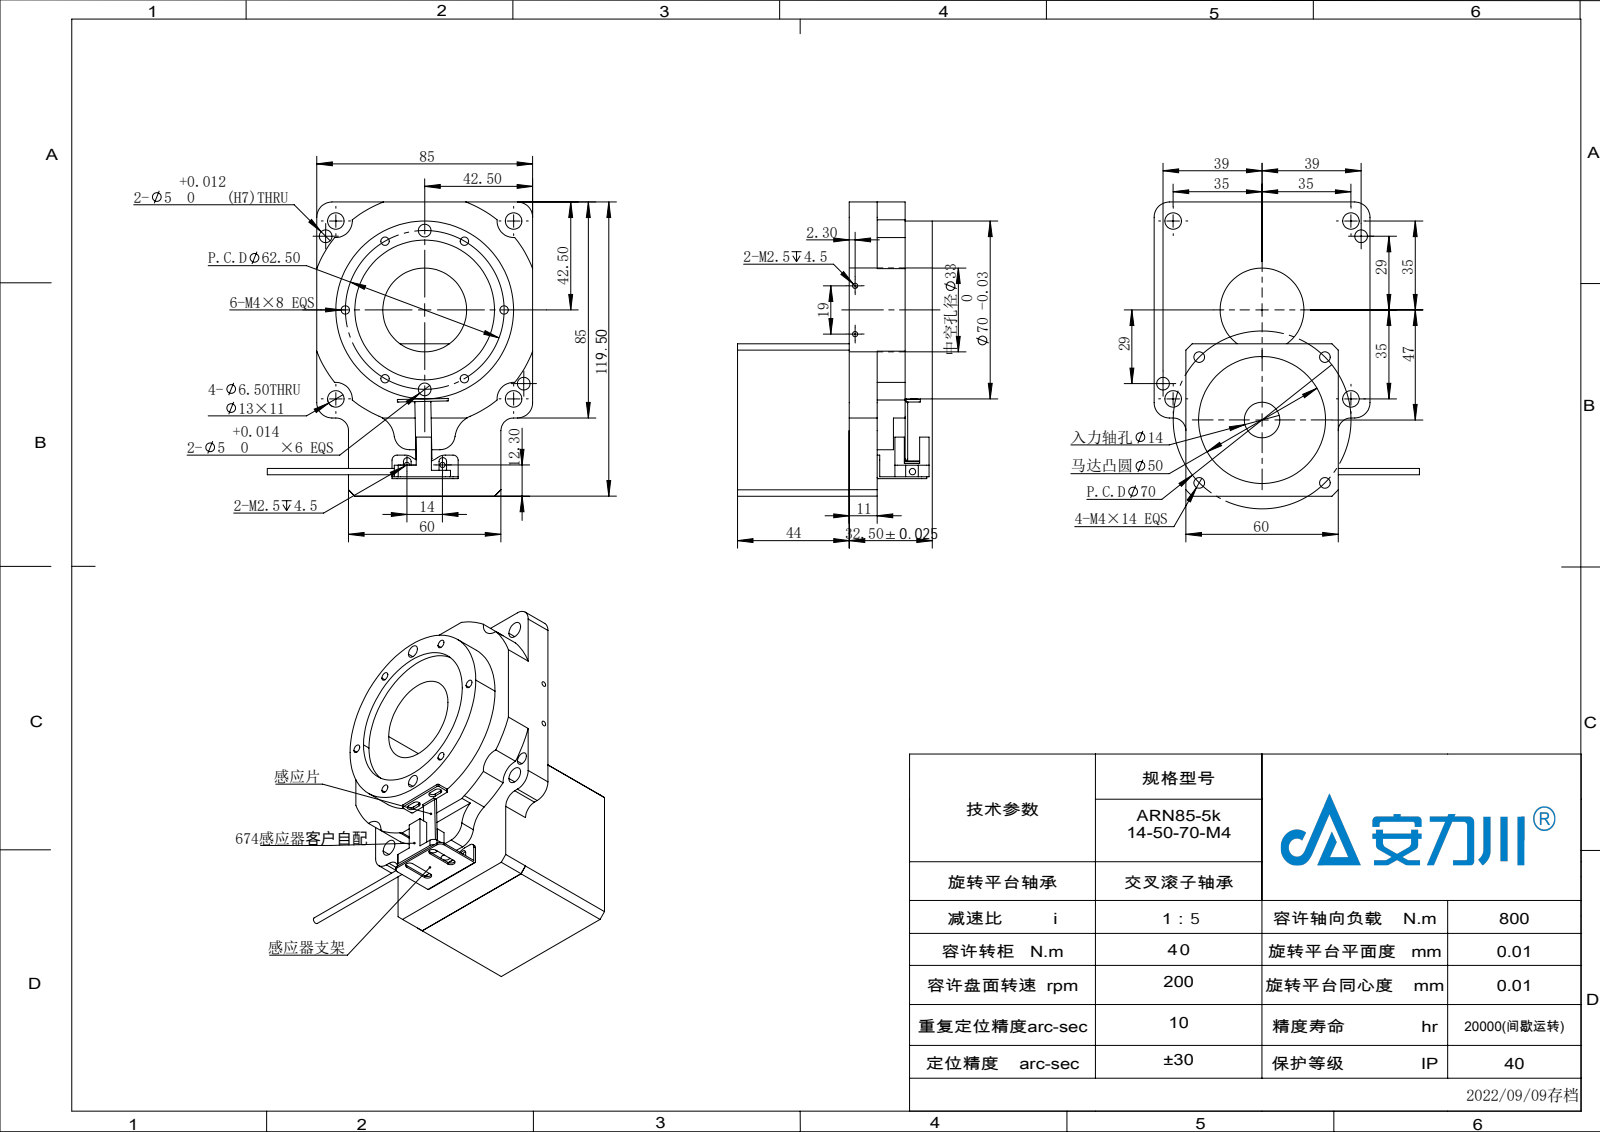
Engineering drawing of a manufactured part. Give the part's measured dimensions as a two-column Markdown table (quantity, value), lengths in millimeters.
| quantity | value |
| --- | --- |
| part name | 感应片1; 感应器支架; KTN85-5K-14-50-70-M4; SX674 |
| STEP written by | SolidWorks 2020 (AUTOMOTIVE_DESIGN) |
| units | millimeters |
| bodies | 4 solids, 278 faces (112 planar, 126 cylindrical, 40 other) |
| overall size | 119.5 × 104.55 × 76.5 |
| volume | 322 311 mm³ |
| surface area | 49 104 mm² |
| round holes (diameter × count) | 3.3 × 10, 2.05 × 6, 5 × 4, 6.5 × 4, 3.5 × 2, 14 × 1, 33 × 1, 50 × 1, 55 × 1 |
| round bosses / shafts (diameter × count) | 70 × 1, 2.5 × 1 |
| partial cylindrical surfaces (radius × count) | 0.5 × 9, 1.5 × 8, 2 × 6, 6 × 6, 1.65 × 4, 5 × 4, 6.5 × 4, 1 × 2 |
| main face-to-face distances | 11, 60, 22, 12.5, 72.5, 50, 39, 61, 5, 44 |
| hole center spacings | 31.25, 35.2, 49.5, 74.93, 70, 31.24, 35, 44.19 |
